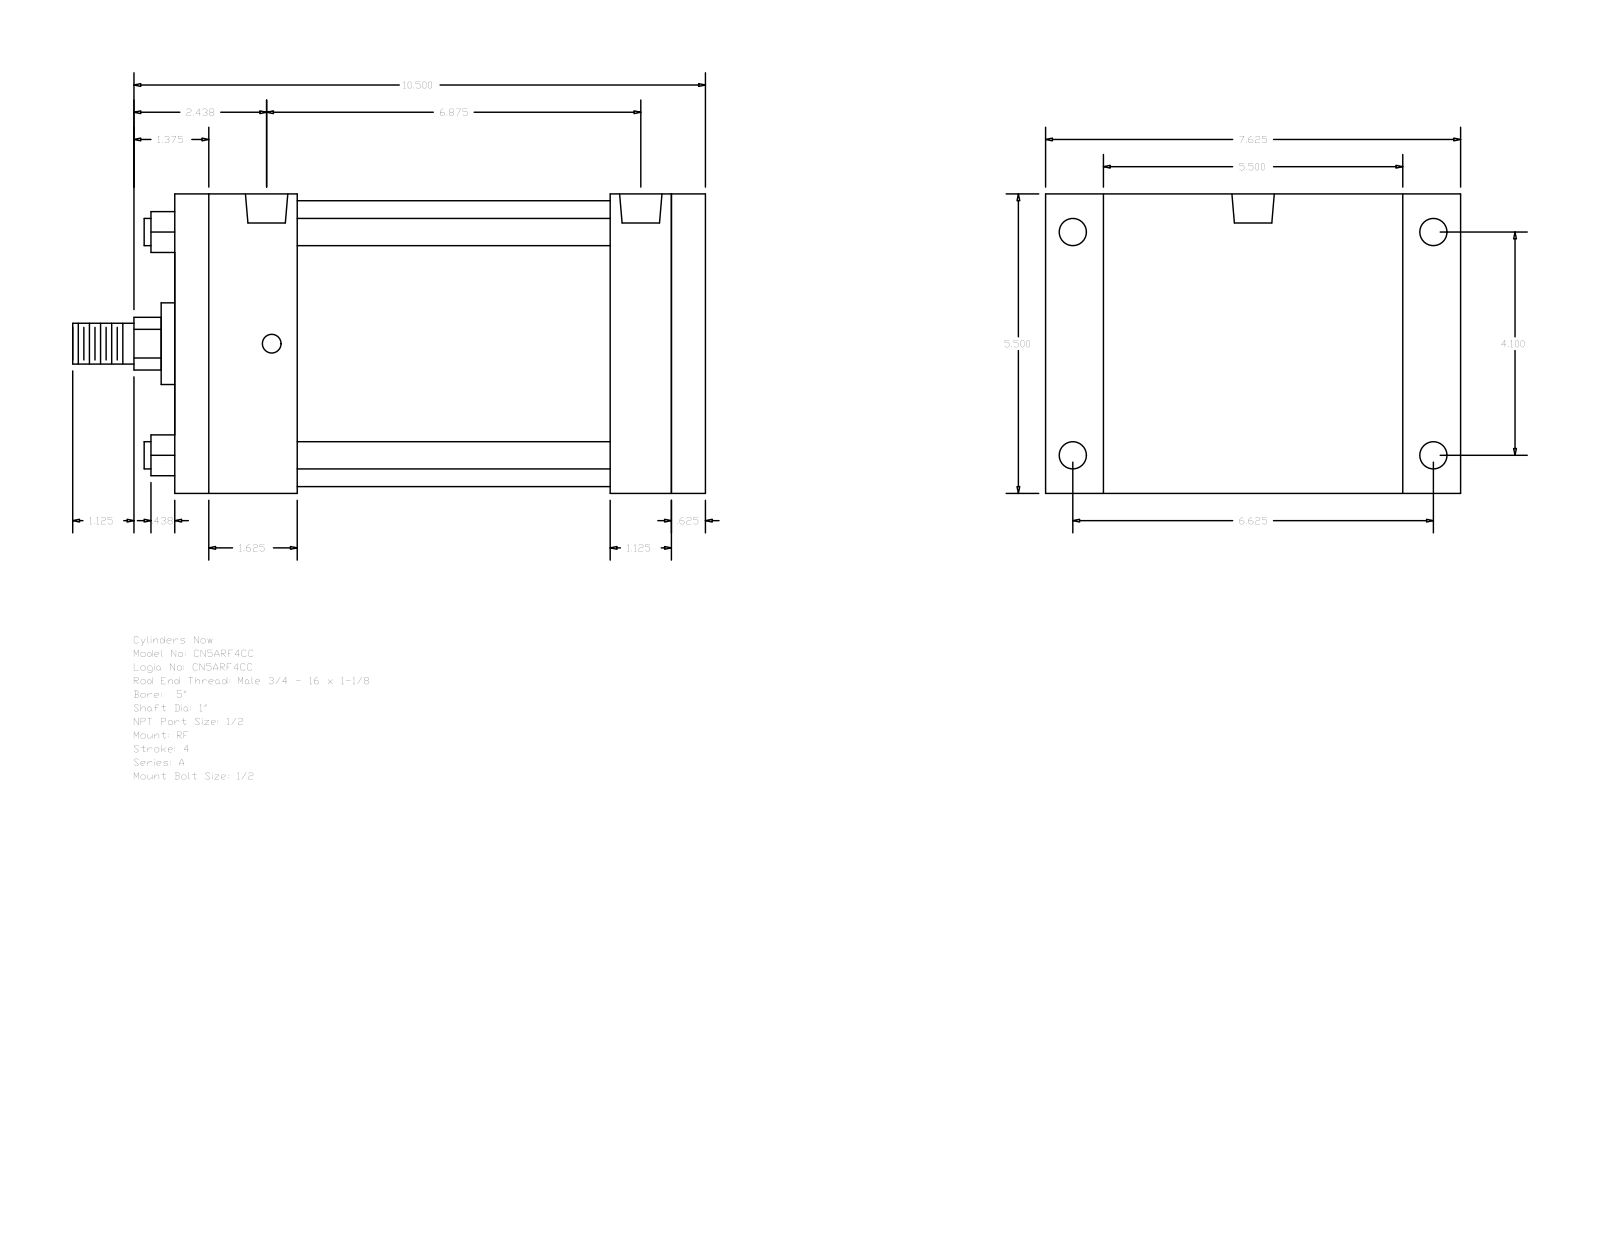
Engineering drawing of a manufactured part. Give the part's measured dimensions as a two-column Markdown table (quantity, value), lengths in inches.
| quantity | value |
| --- | --- |
| part name | A_RF__0500_1 |
| STEP written by | GSSL Pune (CONFIG_CONTROL_DESIGN) |
| units | inches |
| bodies | 0 solids, 92 faces (64 planar, 28 cylindrical, 0 other) |
| overall size | 11.625 × 7.625 × 5.5 |
| round holes (diameter × count) | 0.344 × 4, 0.5 × 4, 0.778 × 2 |
| round bosses / shafts (diameter × count) | 0.5 × 4, 5.25 × 1, 1.5 × 1, 1 × 1, 0.75 × 1 |
| partial cylindrical surfaces (radius × count) | 0.484 × 1 |
| main face-to-face distances | 5.5, 9.75, 9.125, 0.625, 1.125, 2.25, 6.875, 7.5, 8, 5.75 |
| hole center spacings | 0.094, 4.1, 6.625, 6.687, 6.781, 7.791, 6.875 |
